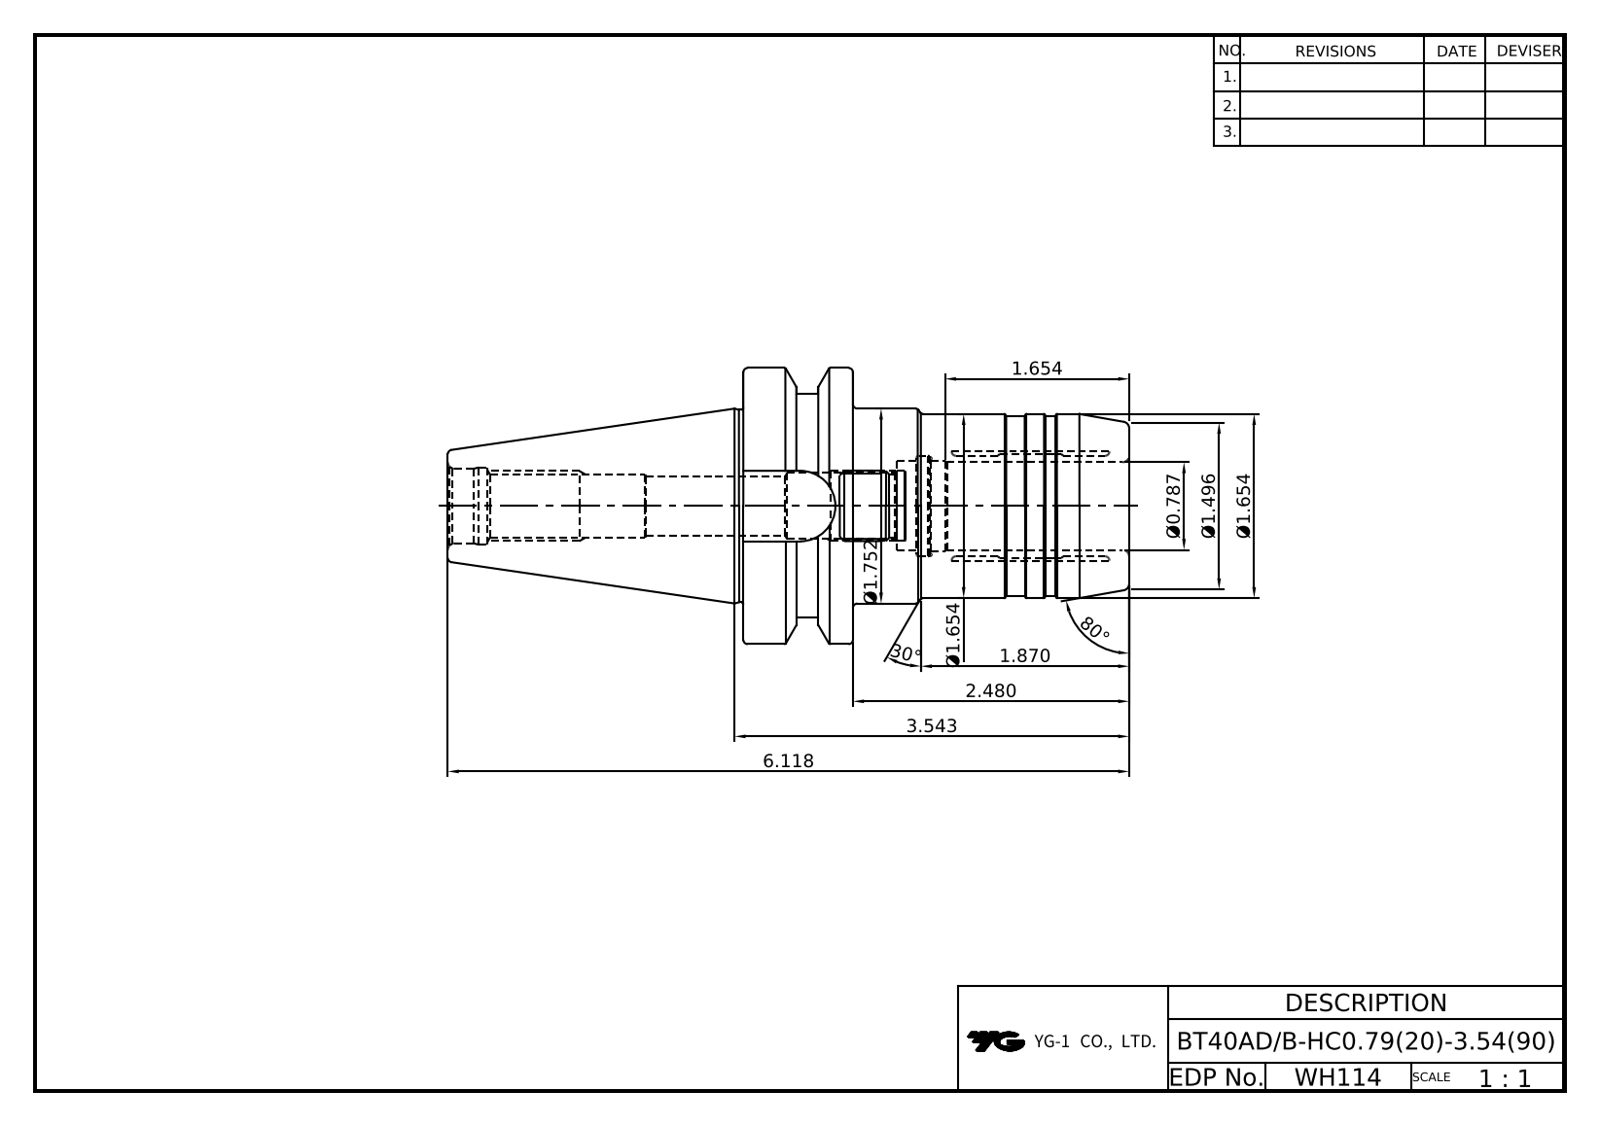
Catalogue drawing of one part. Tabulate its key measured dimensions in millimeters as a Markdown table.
| quantity | value |
| --- | --- |
| part name | BT40ADB-HC20-90 |
| STEP written by | Autodesk Inventor 2020 (AUTOMOTIVE_DESIGN) |
| units | millimeters |
| bodies | 1 solid, 90 faces (21 planar, 33 cylindrical, 36 other) |
| overall size | 155.4 × 63 × 63 |
| volume | 188 266 mm³ |
| surface area | 35 103 mm² |
| round holes (diameter × count) | 3.24 × 4, 4 × 4, 13.5 × 1, 13.84 × 1, 17 × 1, 17.6 × 1, 20 × 1, 20.4 × 1 |
| round bosses / shafts (diameter × count) | 63 × 1, 51 × 1, 44.5 × 1, 44 × 1, 42 × 1, 41 × 1 |
| partial cylindrical surfaces (radius × count) | 8.05 × 1 |
| main face-to-face distances | 25, 88, 63, 45.2, 17.1, 7.9, 70.9, 12.1, 5, 12.9 |
